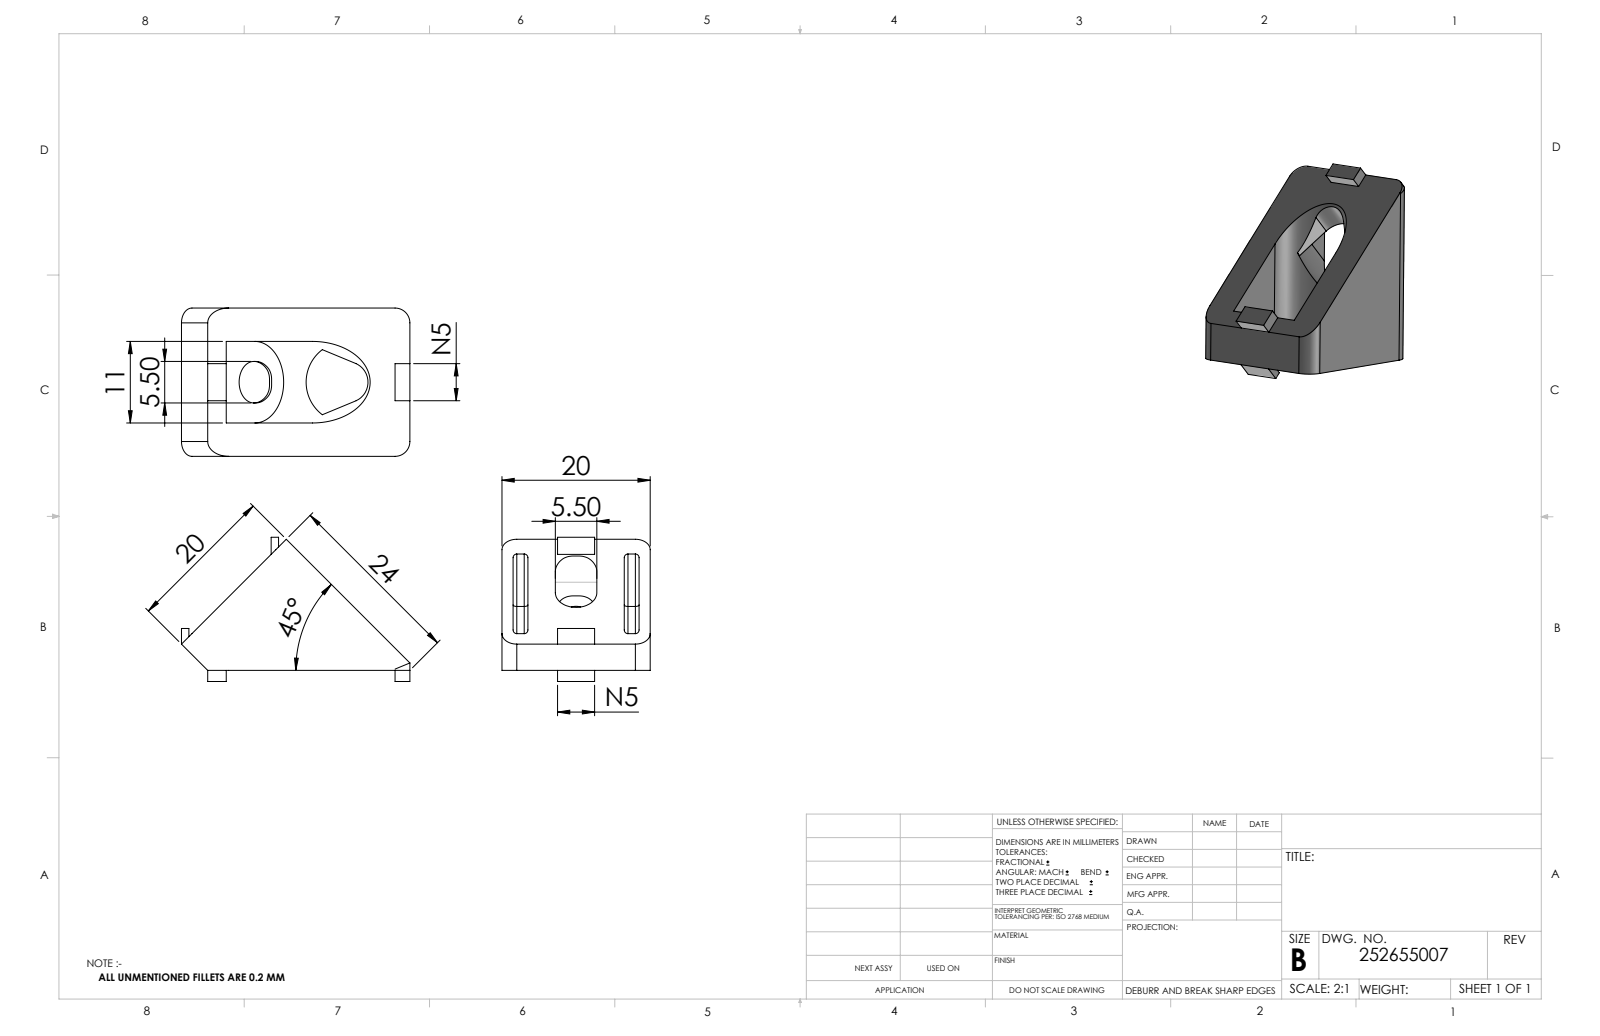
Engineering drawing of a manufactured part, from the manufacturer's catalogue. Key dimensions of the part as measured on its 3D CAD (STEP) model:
Part name (STEP PRODUCT): 252655007_c_1
STEP written by: SolidWorks 2014 (CONFIG_CONTROL_DESIGN)
Units: millimetres
Bodies: 1 solid, 70 faces (44 planar, 24 cylindrical, 2 other)
Overall size (bounding box): 26.99 × 21.06 × 20
Volume: 3 897 mm³ · Surface area: 2 716 mm²
Partial cylindrical surfaces — rounded edges, fillets, slot ends (radius × count): R0.5 ×12, R2 ×6, R5.5 ×2, R2.75 ×1
Main face-to-face distances: 20, 4, 4.5, 15.5, 1.5, 1, 3, 2, 11, 3.5
